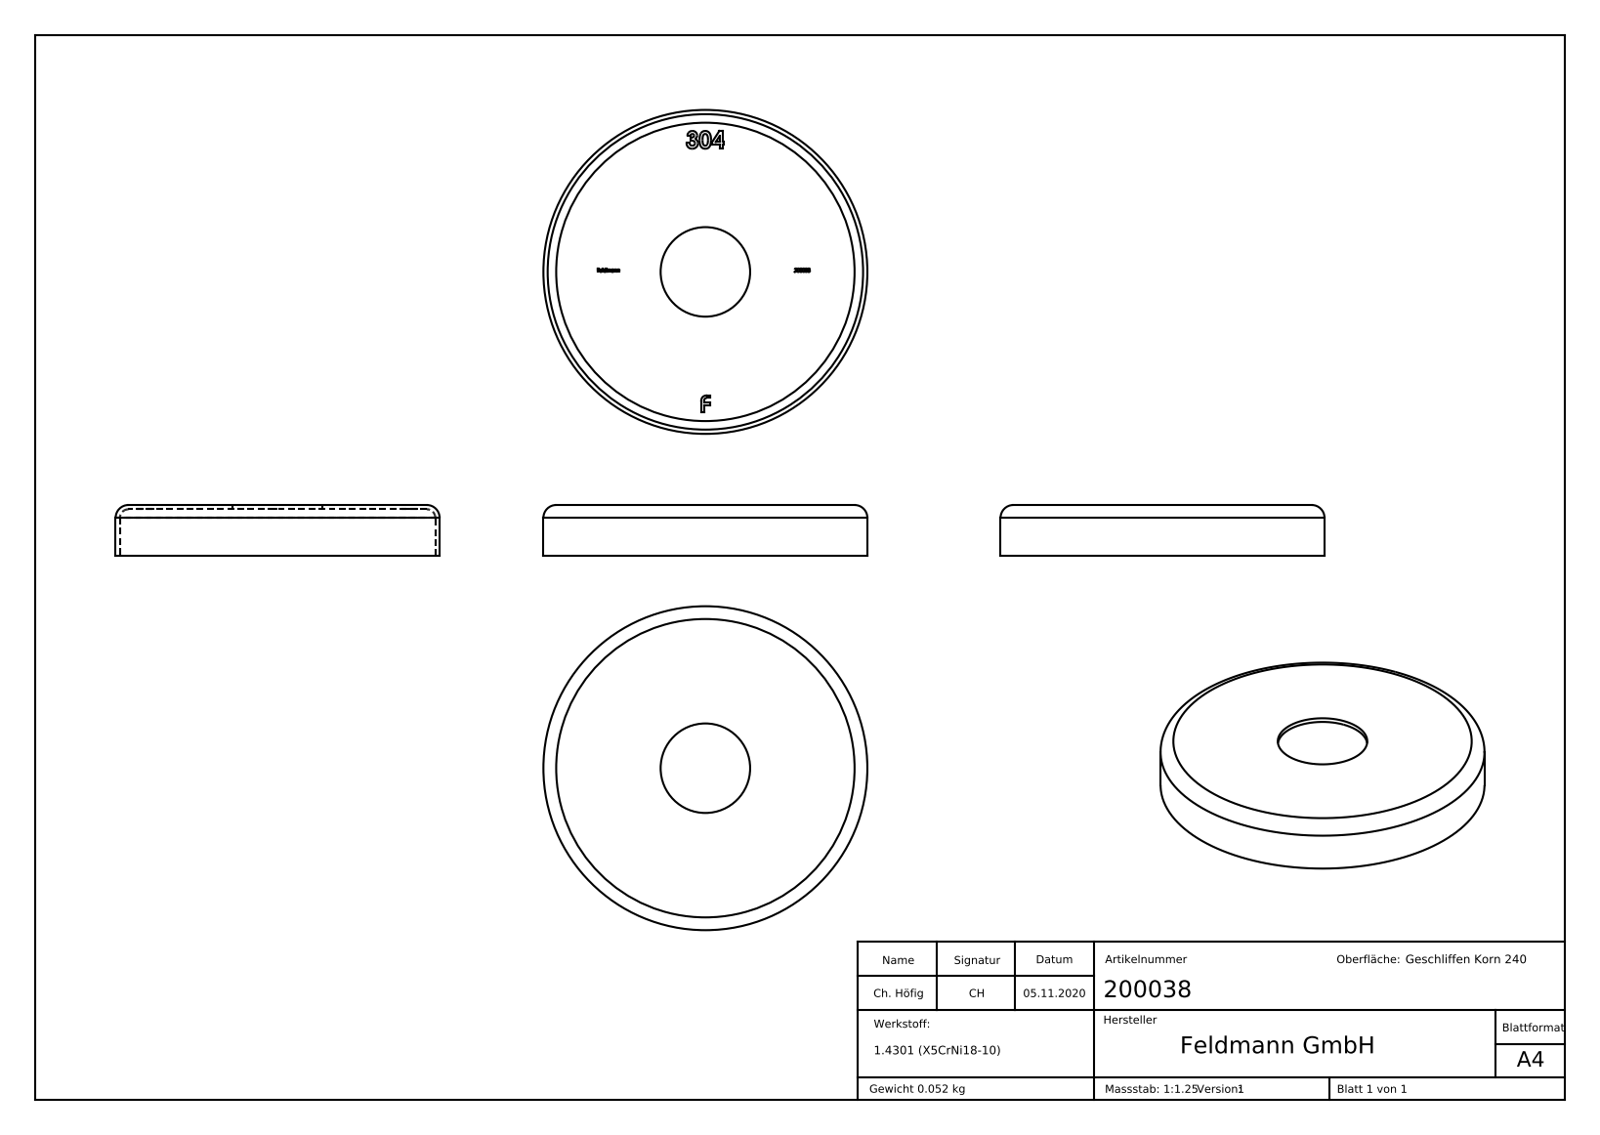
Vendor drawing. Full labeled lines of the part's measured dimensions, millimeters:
Part name (STEP PRODUCT): 200038
STEP written by: SolidWorks 2018 (CONFIG_CONTROL_DESIGN)
Units: millimetres
Bodies: 1 solid, 268 faces (121 planar, 6 cylindrical, 141 other)
Overall size (bounding box): 76 × 76 × 12
Volume: 6 524 mm³ · Surface area: 13 368 mm²
Round holes (diameter × count): ⌀21 ×1, ⌀74 ×1
Round bosses / shafts (diameter × count): ⌀76 ×1
Main face-to-face distances: 1, 11, 12, 11.1, 0.9, 0.71, 5, 0.58, 1.78, 4.29
